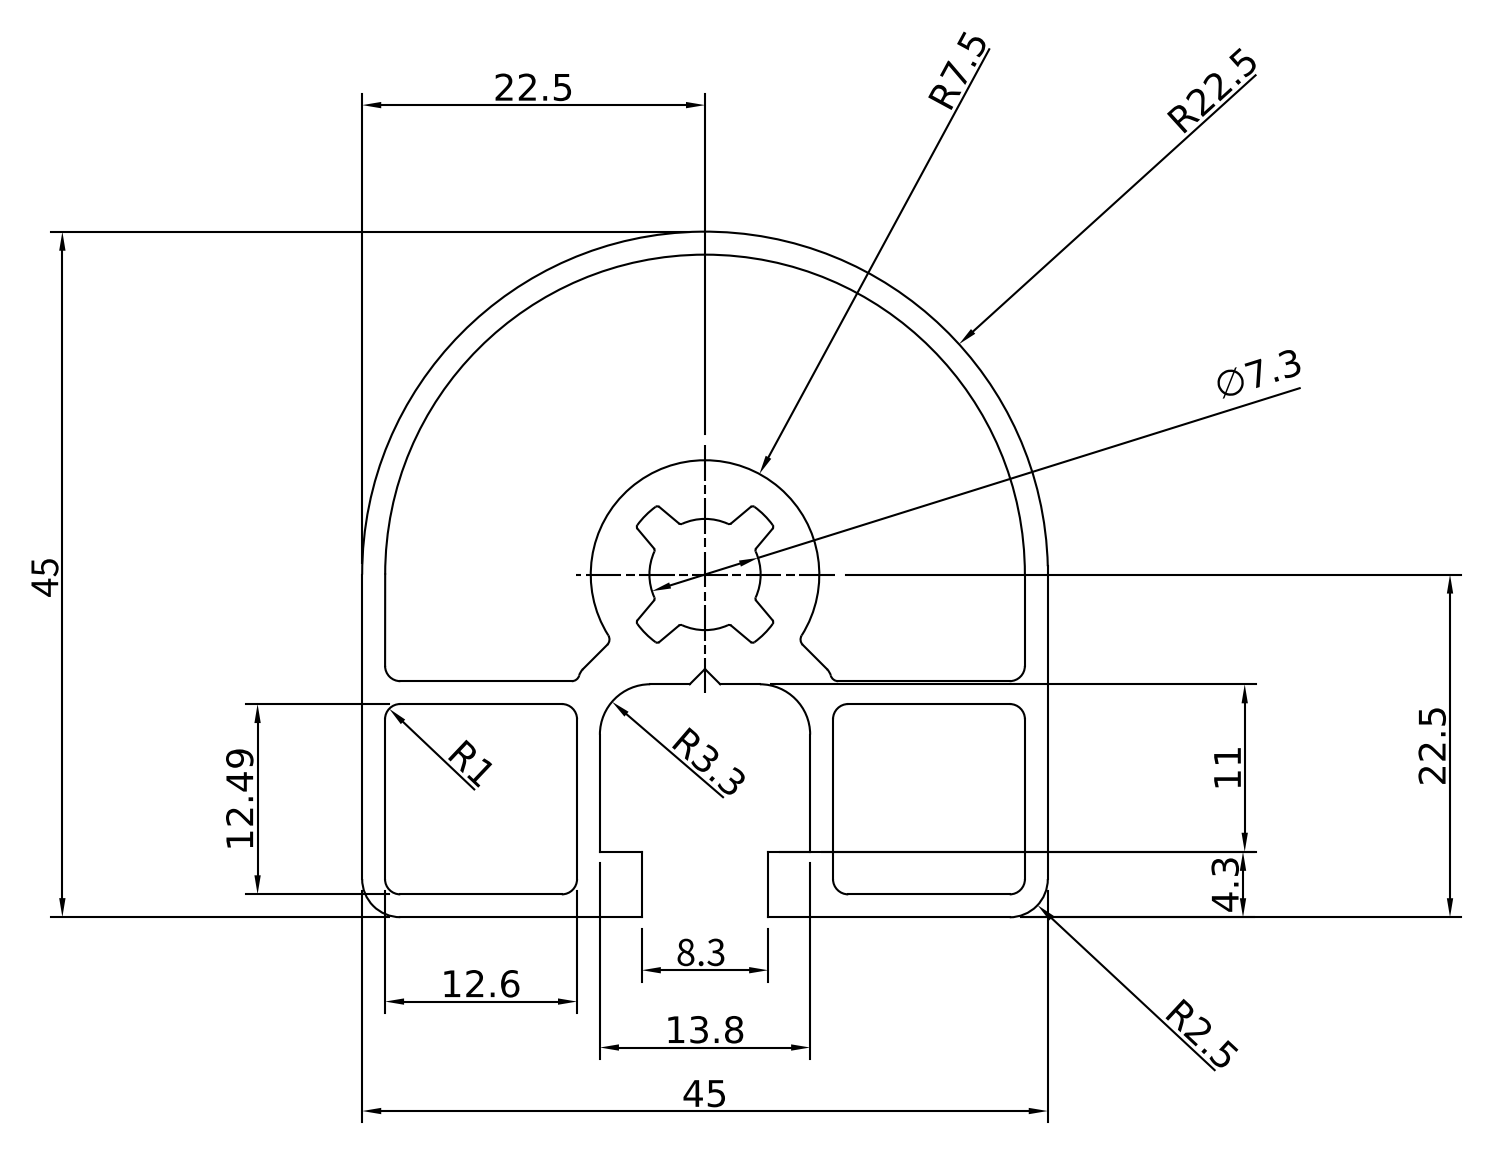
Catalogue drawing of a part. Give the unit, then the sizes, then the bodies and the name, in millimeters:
Units: millimetres
Overall size (bounding box): 1000 × 45 × 45
Partial cylindrical surfaces — rounded edges, fillets, slot ends (radius × count): R0.2 ×16, R1 ×12, R0.5 ×4, R2.5 ×2, R3.3 ×2, R3.65 ×1, R5.5 ×1, R7.5 ×1
Main face-to-face distances: 1.5, 13.99, 14.1, 29.4, 1.51, 12.49, 30.9, 43.5, 12.6, 15.3
Volume: 453 549 mm³ · Surface area: 476 233 mm²
Bodies: 1 solid, 85 faces (38 planar, 47 cylindrical, 0 other)
Part name (STEP PRODUCT): BPRDD0000144
STEP written by: Autodesk Inventor 2019 (AUTOMOTIVE_DESIGN)
